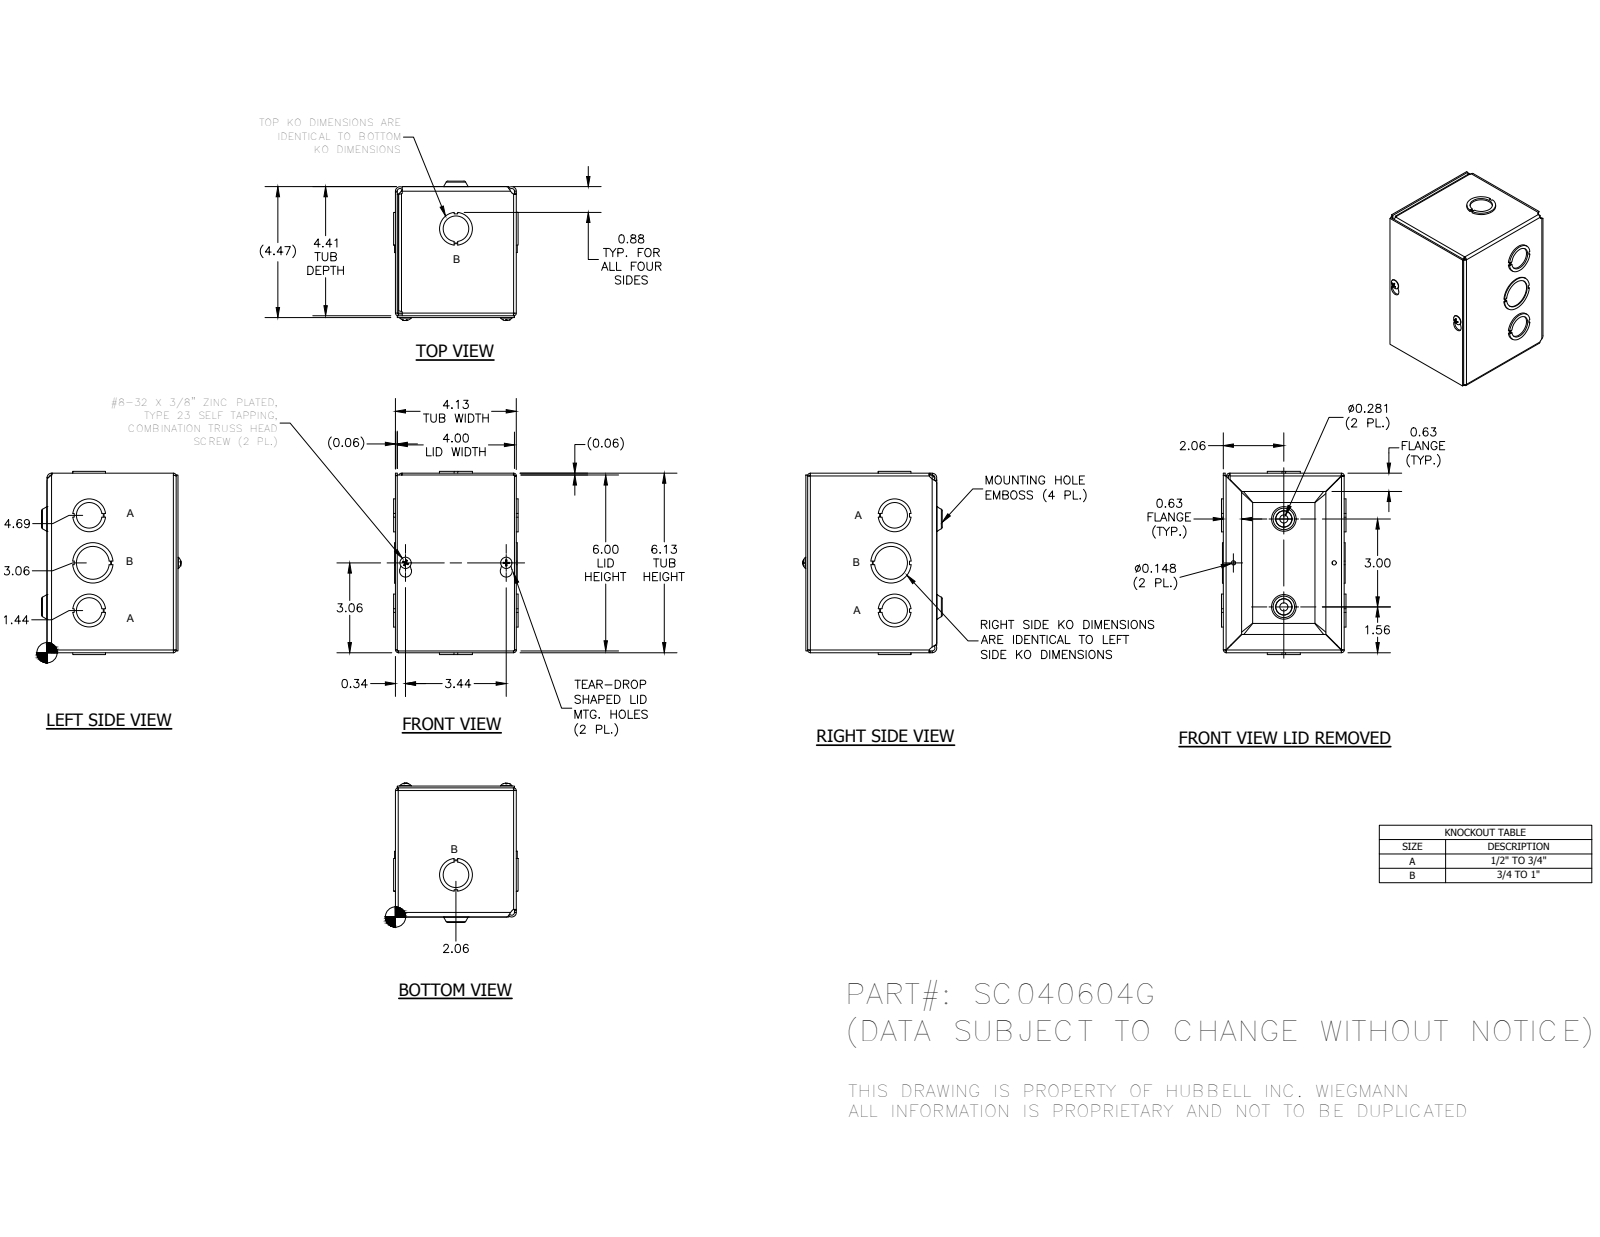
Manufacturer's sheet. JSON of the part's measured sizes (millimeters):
{"part_name": "SC0406GBKP; SC040604GWRA; SC0406GLID; 34056 (+1 more)", "step_written_by": "Autodesk Inventor 2014 (AUTOMOTIVE_DESIGN)", "units": "millimeters", "bodies": {"solids": 16, "faces": 507, "planar": 289, "cylindrical": 107, "other": 111}, "overall_size": [158.72, 120.78, 107.92], "round_holes": [[28.57, 4], [22.22, 3], [3.76, 2], [7.14, 2], [34.92, 1]], "round_bosses_or_shafts": [[9.75, 2], [4.17, 2]], "partial_cylinders_radius": [[0.79, 8], [2.37, 8], [1.4, 4], [1.57, 4], [2.38, 4], [2.79, 4], [2.97, 4], [3.15, 4]], "face_to_face_distances": [1.57, 1.58, 110.32, 104.78, 103.2, 103.21, 111.89, 101.63, 1.59, 111.91], "hole_center_spacings": [57.94, 57.95, 41.39, 41.4, 76.2, 82.55, 87.31]}
